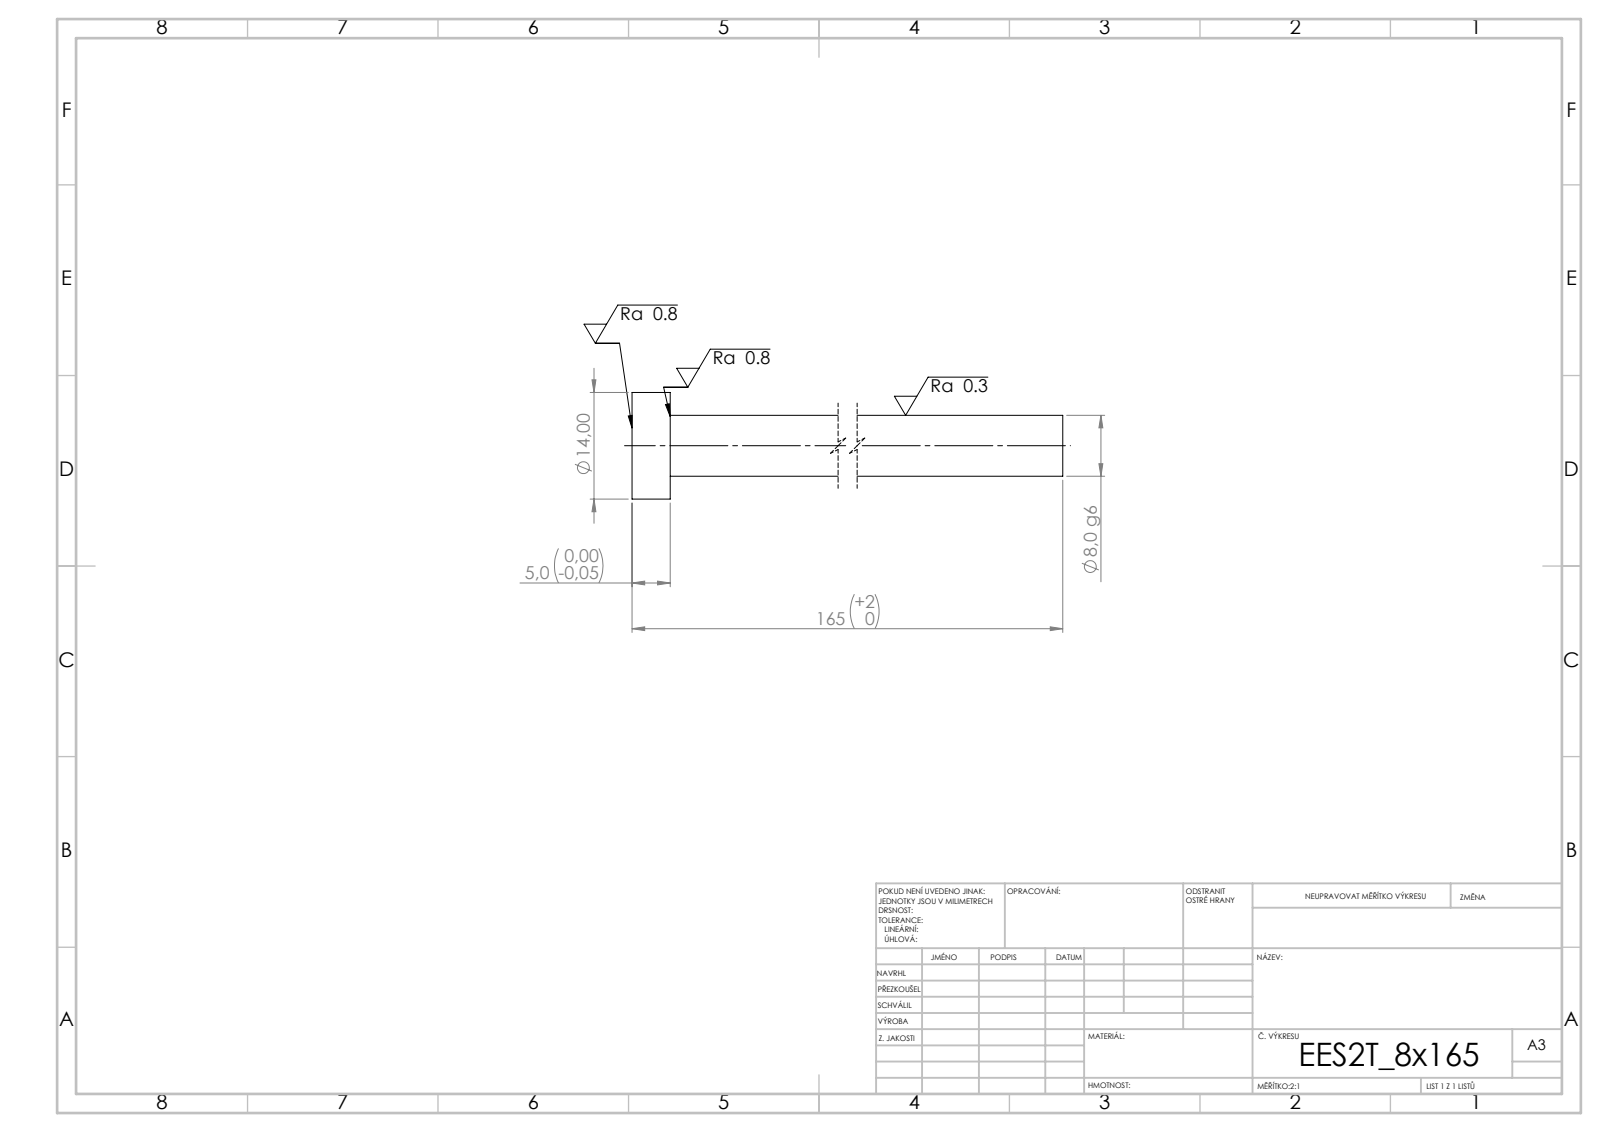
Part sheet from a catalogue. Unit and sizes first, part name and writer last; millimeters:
Units: millimetres
Overall size (bounding box): 165 × 14 × 14
Round bosses / shafts (diameter × count): ⌀14 ×1, ⌀8 ×1
Main face-to-face distances: 5, 165, 160
Volume: 8 812 mm³ · Surface area: 4 549 mm²
Bodies: 1 solid, 7 faces (3 planar, 4 cylindrical, 0 other)
STEP written by: SolidWorks 2019 (CONFIG_CONTROL_DESIGN)
